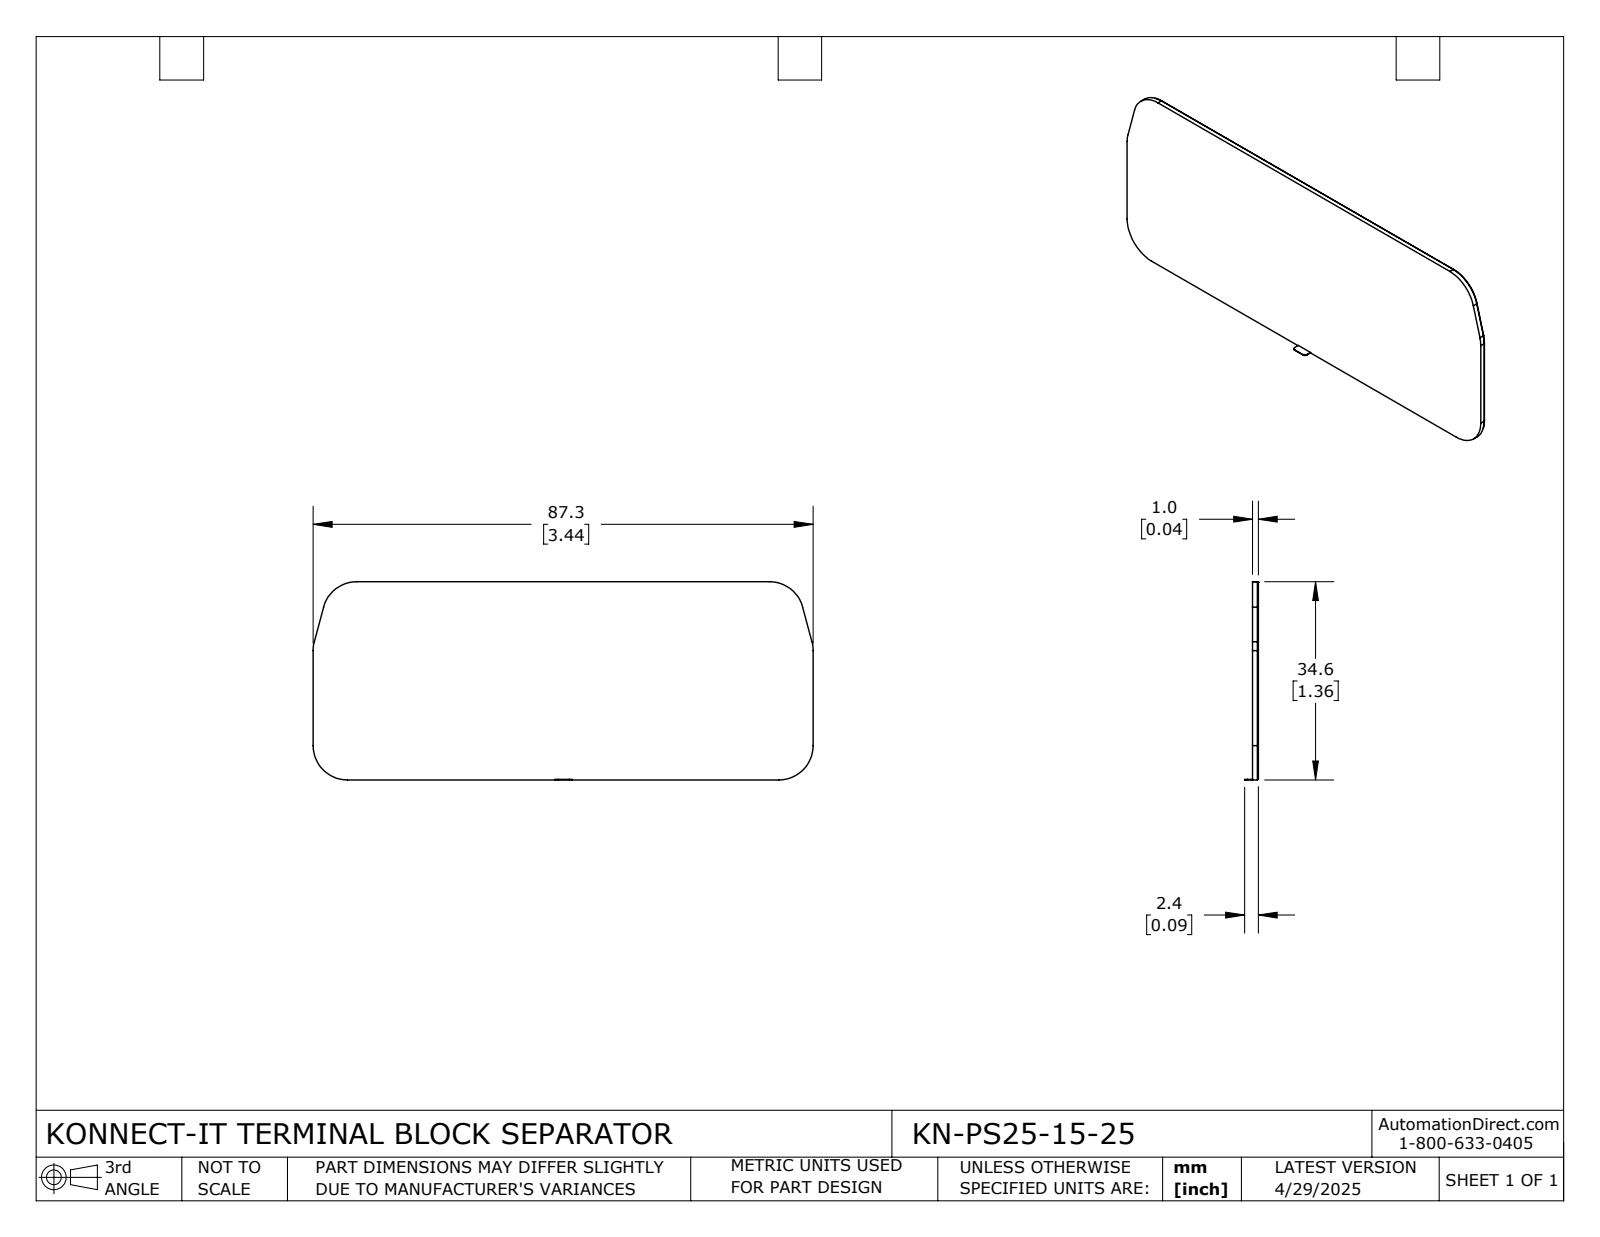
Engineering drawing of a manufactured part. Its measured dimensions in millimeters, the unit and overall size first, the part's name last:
Units: millimetres
Overall size (bounding box): 87.31 × 34.61 × 2.4
Partial cylindrical surfaces — rounded edges, fillets, slot ends (radius × count): R5.9 ×6, R6 ×6, R0.5 ×2
Main face-to-face distances: 1, 34.61, 34.51, 0.85, 87.31, 34.41, 87.21, 87.11, 1.4, 2.25
Volume: 2 961 mm³ · Surface area: 6 168 mm²
Bodies: 1 solid, 33 faces (19 planar, 14 cylindrical, 0 other)
Part name (STEP PRODUCT): KN-PS25-15-25
STEP written by: SolidWorks 2024 (CONFIG_CONTROL_DESIGN)
